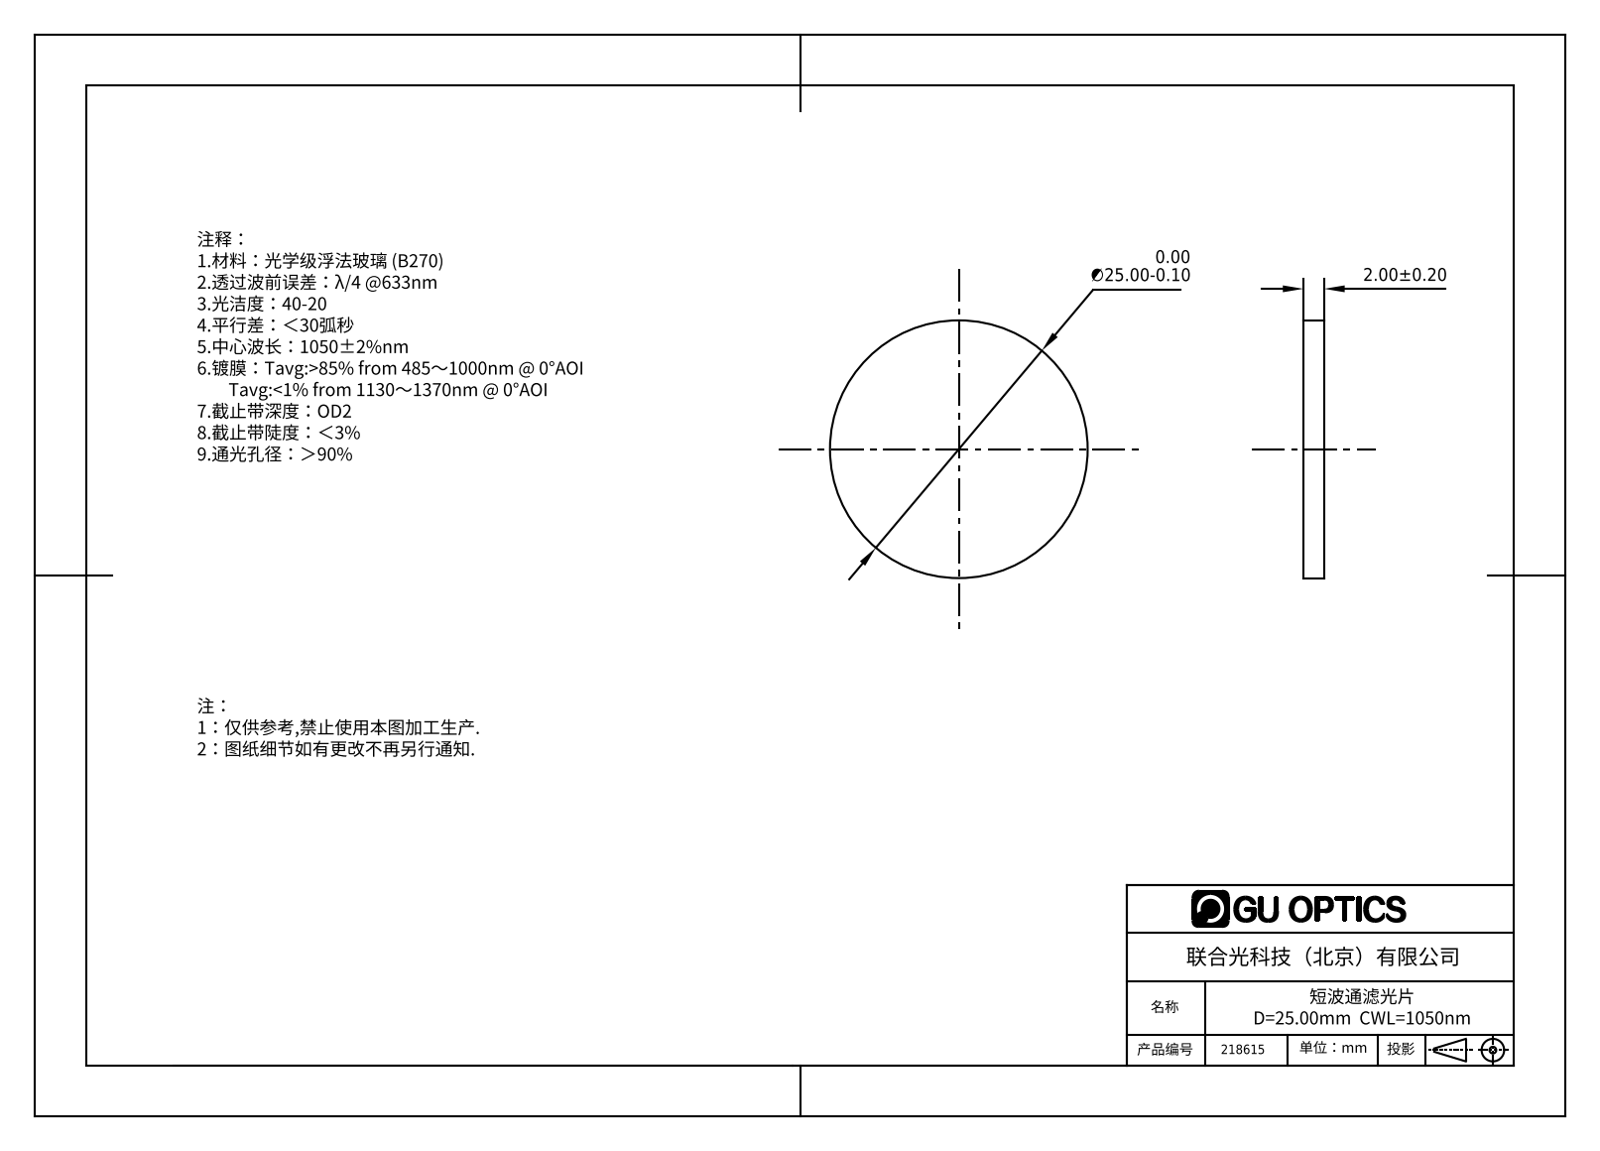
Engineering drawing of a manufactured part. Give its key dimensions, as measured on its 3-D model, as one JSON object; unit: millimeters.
{"part_name": "218602", "step_written_by": "SolidWorks 2016 (AUTOMOTIVE_DESIGN)", "units": "millimeters", "bodies": {"solids": 1, "faces": 4, "planar": 2, "cylindrical": 2, "other": 0}, "overall_size": [25, 25, 2], "volume_mm3": 982, "surface_area_mm2": 1139, "round_bosses_or_shafts": [[25, 1]], "face_to_face_distances": [2]}
